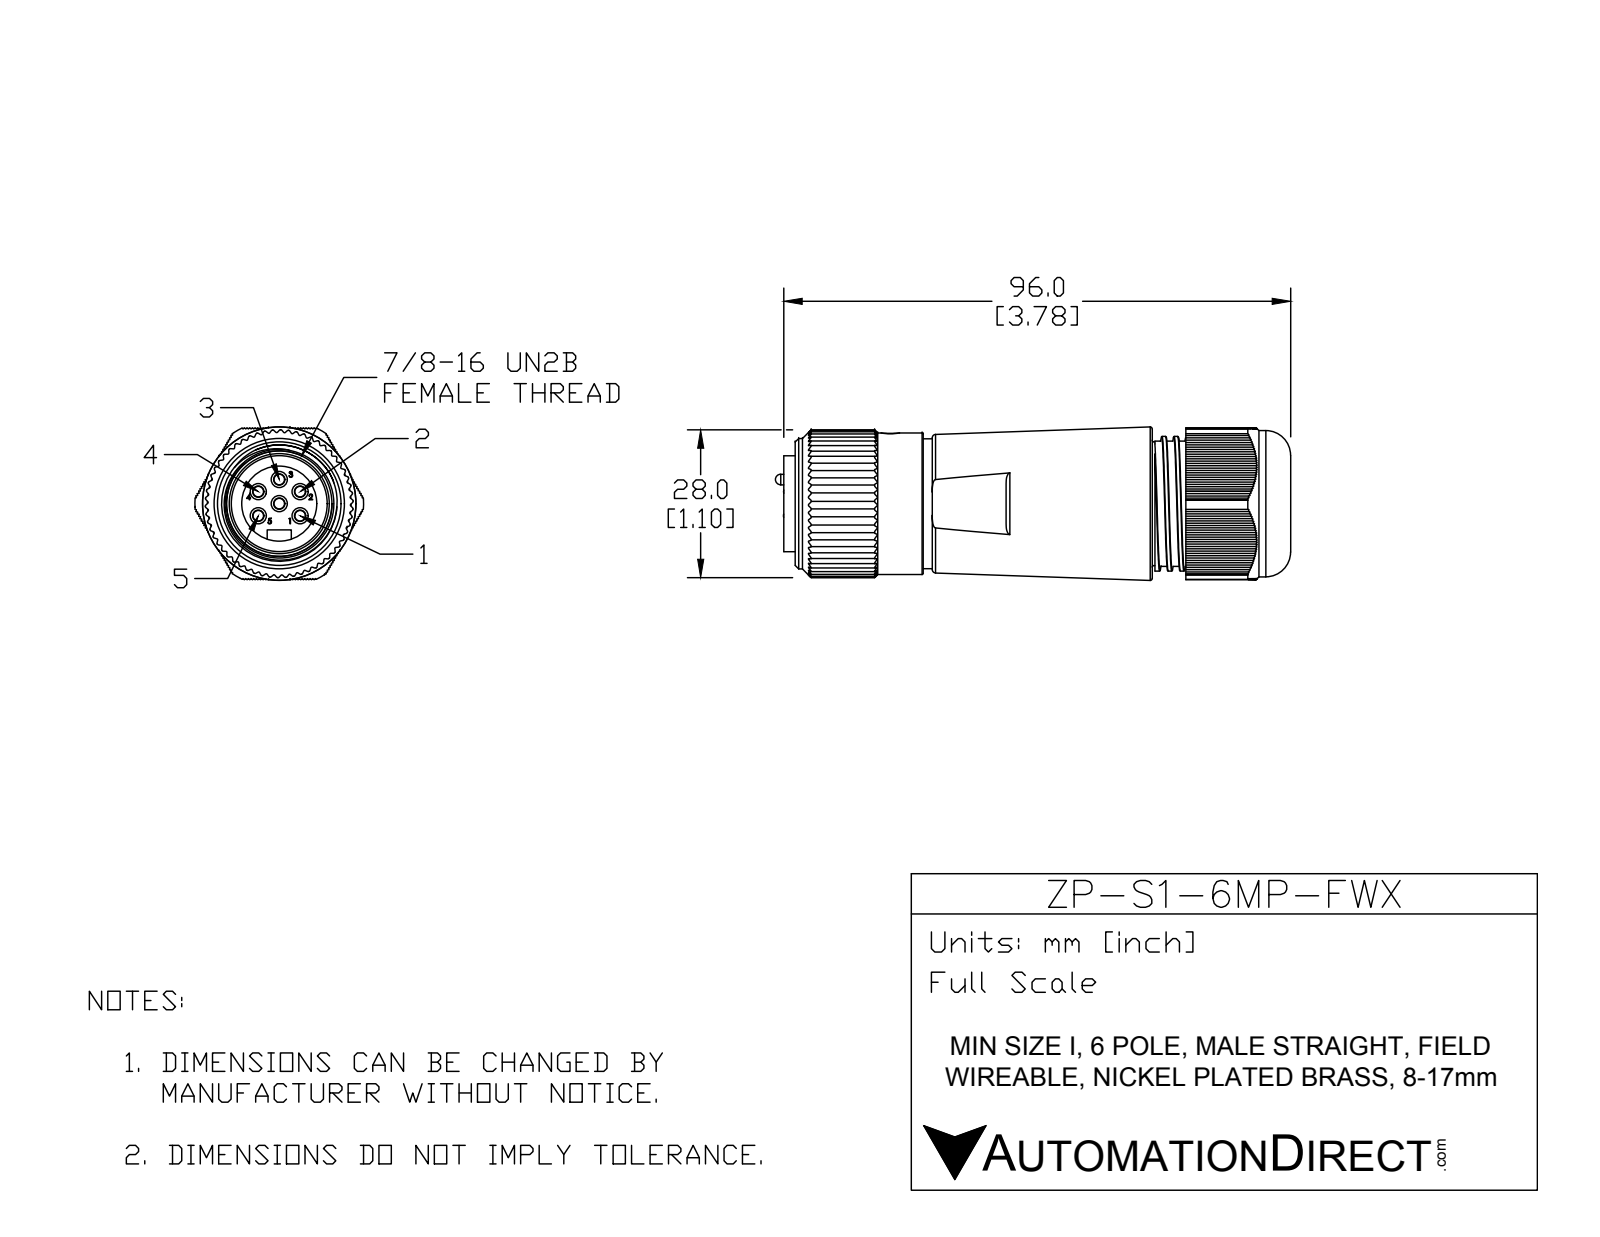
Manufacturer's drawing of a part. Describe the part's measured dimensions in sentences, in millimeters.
The part is named "ZP-S1-6MP-FWX". Its 3-D file was written by "SolidWorks 2015 (AUTOMOTIVE_DESIGN)". It is 10 solids with 937 faces: 528 planar, 318 cylindrical and 91 other. Overall it measures 97.55 by 31.9 by 29.06 millimeters. Its volume is 49 686 cubic millimeters and its surface area 17 119 square millimeters. Round holes: 1 of diameter 3.56, 1 of diameter 14.22, 1 of diameter 17.27, 1 of diameter 20.58, 1 of diameter 21.57, 1 of diameter 24.2, 1 of diameter 25.4. Round bosses or shafts: 6 of diameter 3.15, 6 of diameter 2, 1 of diameter 27.69, 1 of diameter 26.8, 1 of diameter 25.5, 1 of diameter 24.68, 1 of diameter 24.3, 1 of diameter 18.14. Partial cylindrical surfaces (rounded edges, fillets, slot ends): 165 of radius 0.25, 1 of radius 2.29, 1 of radius 14, 1 of radius 15.95. The main face-to-face distances are 68.61, 1.06, 0.35, 0.71, 1.41, 2.12, 1.77, 8.79, 59.82, 20.52.
